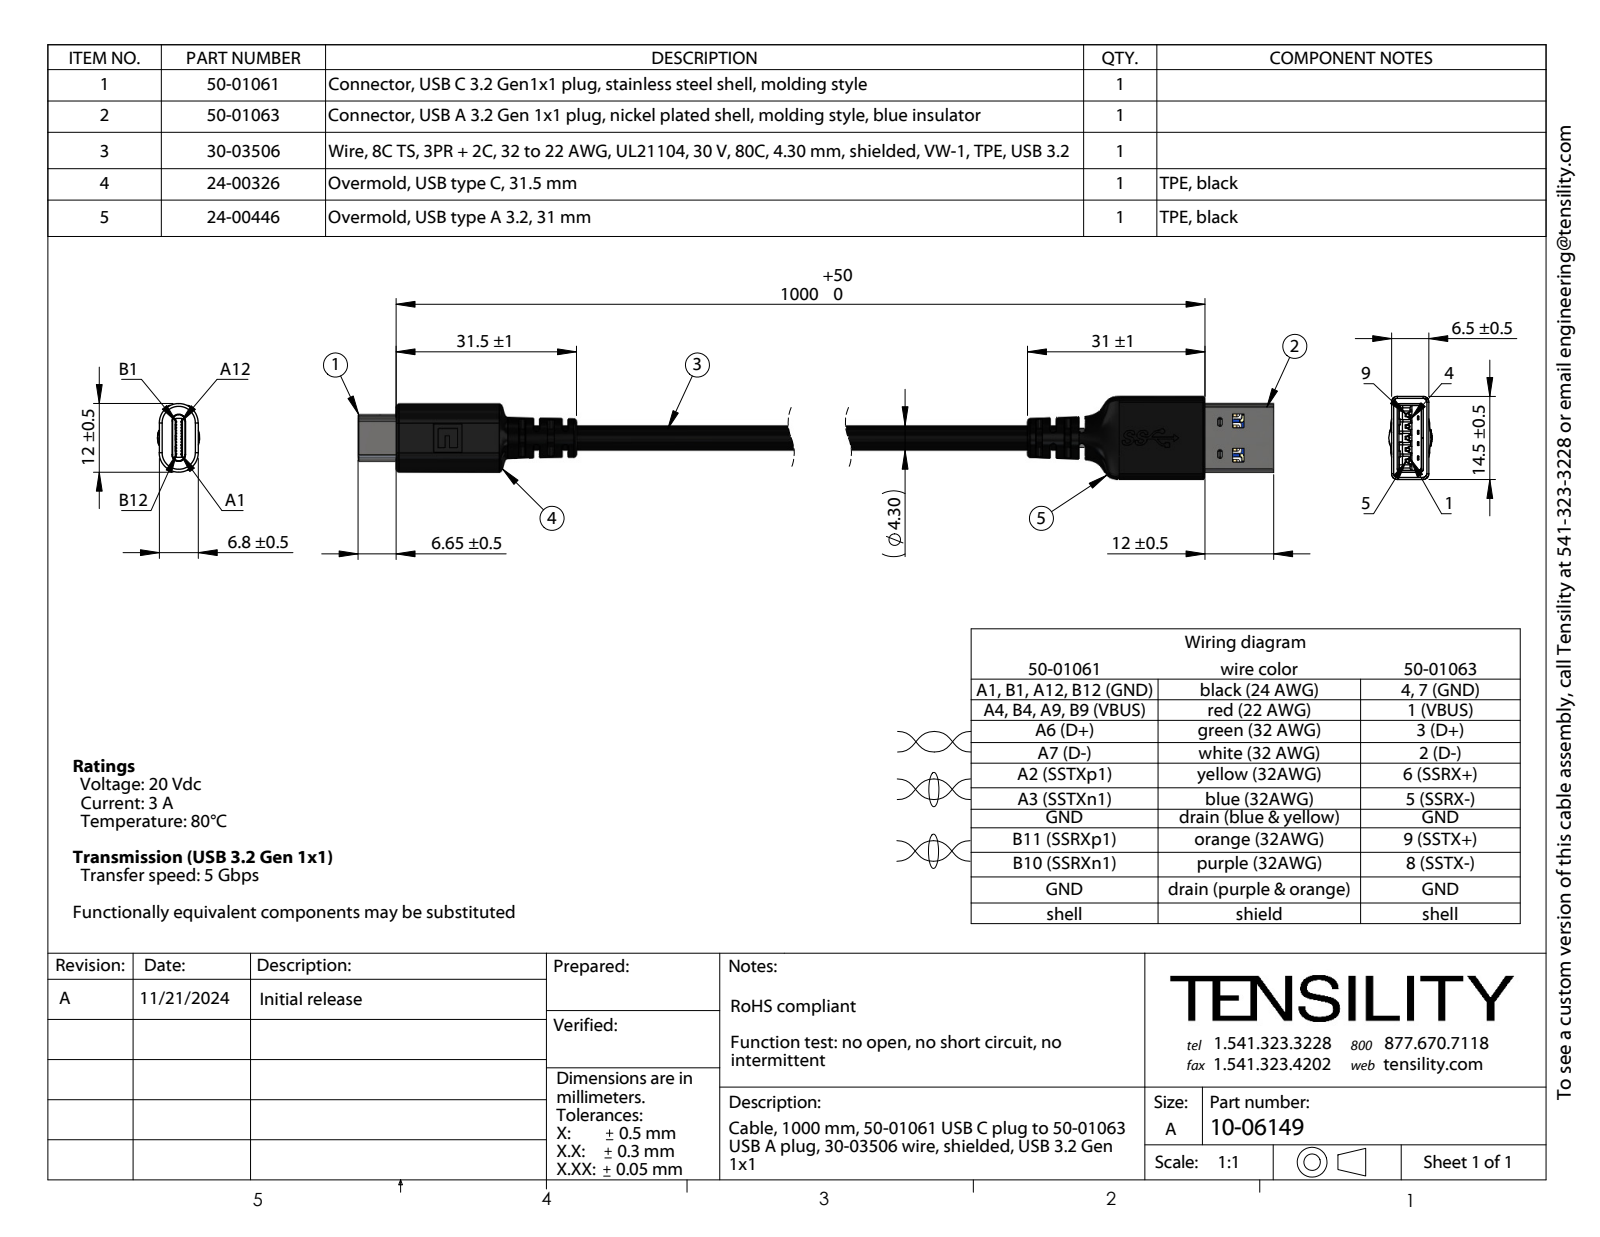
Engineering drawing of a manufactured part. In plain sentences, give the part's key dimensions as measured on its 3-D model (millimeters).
The part is named "50-01063_shell; 50-01063_pin4; 50-01063_pin1; 50-01063 (+8 more)". Its 3-D file was written by "SolidWorks 2021 (CONFIG_CONTROL_DESIGN)". It is 184 solids with 2646 faces: 1399 planar, 829 cylindrical and 418 other. Overall it measures 211.15 by 14.5 by 7.54 millimeters. Its volume is 5 792 cubic millimeters and its surface area 26 919 square millimeters. Round holes: 1 of diameter 0.87, 1 of diameter 3.23, 1 of diameter 3.35. Round bosses or shafts: 4 of diameter 0.6, 2 of diameter 0.75, 2 of diameter 0.55, 2 of diameter 0.45, 1 of diameter 4.3, 1 of diameter 3.25, 1 of diameter 1.66, 1 of diameter 1. Partial cylindrical surfaces (rounded edges, fillets, slot ends): 30 of radius 0.1, 24 of radius 0.2, 20 of radius 0.5, 13 of radius 0.3, 10 of radius 0.4, 9 of radius 0.25, 7 of radius 0.35, 7 of radius 0.6. The main face-to-face distances are 0.89, 4.25, 0.9, 2.5, 0.35, 6.5, 0.88, 3.1, 1.28, 0.98. The hole center spacings are 0.32, 0.33, 0.37, 0.36, 0.44, 0.42, 1.56, 1.67.
